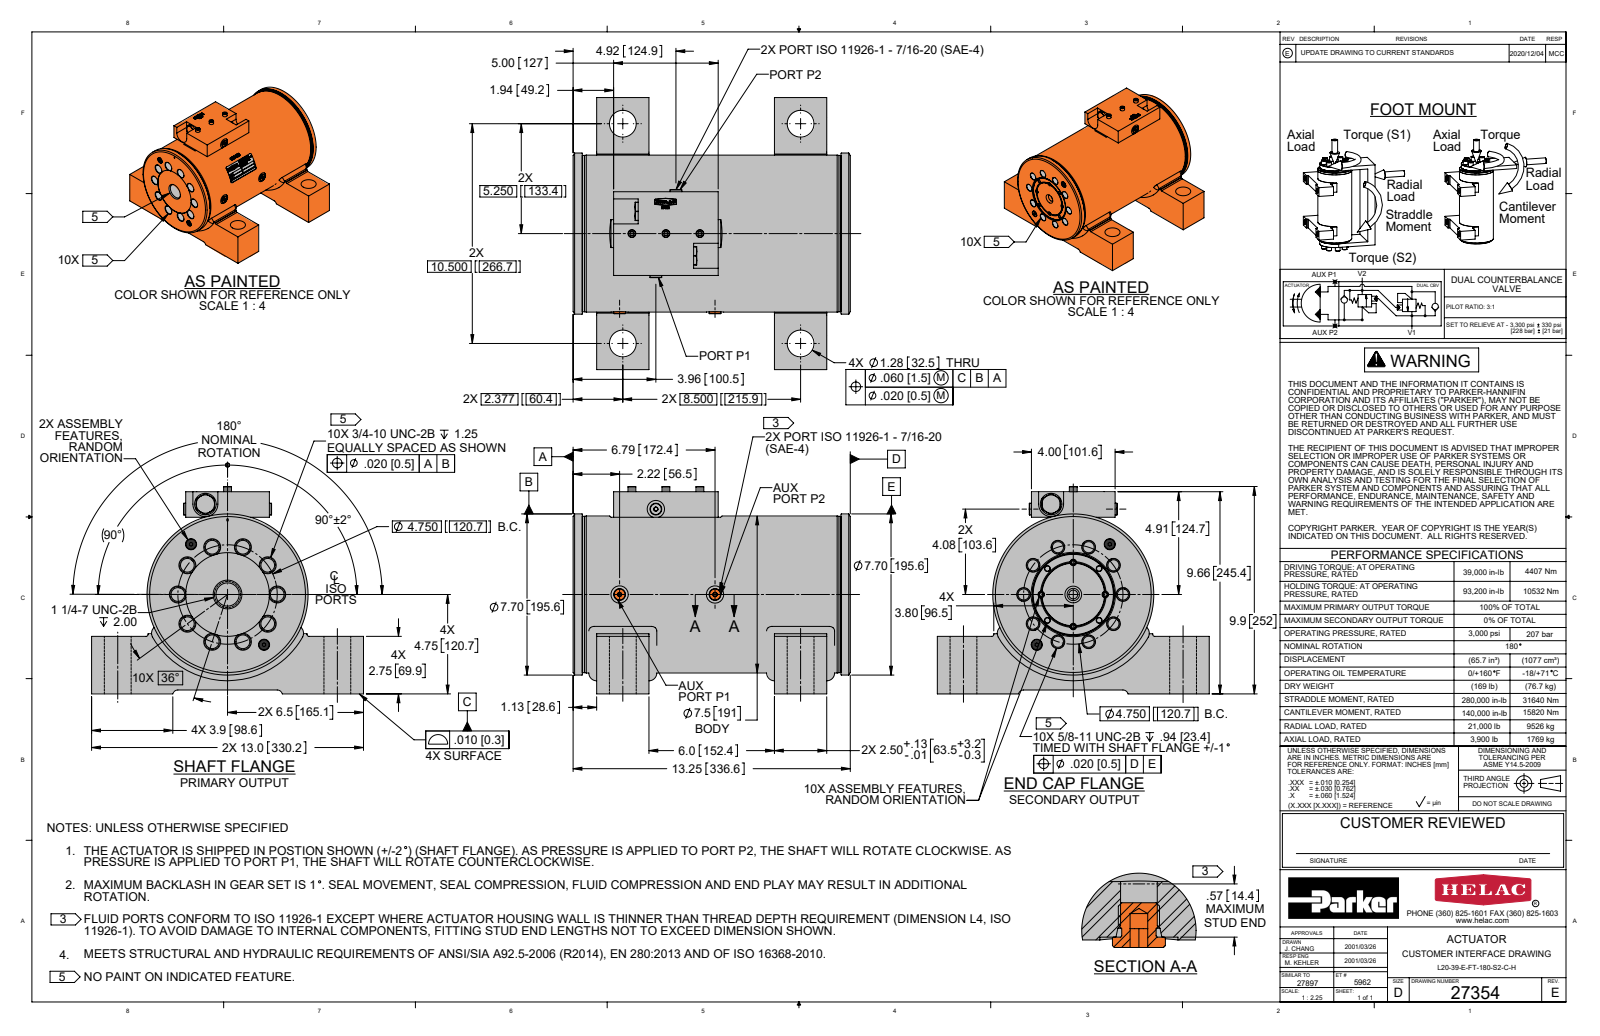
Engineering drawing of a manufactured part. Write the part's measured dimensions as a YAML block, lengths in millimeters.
part_name: "27354-CM.CYL"
step_written_by: "SolidWorks 2018 (AUTOMOTIVE_DESIGN)"
units: millimeters
bodies: {solids: 30, faces: 2219, planar: 515, cylindrical: 805, other: 899}
overall_size: [336.6, 330.2, 251.7]
volume: 12400000
surface_area: 1265000
round_holes:
  - {diameter: 13.5, count: 10}
  - {diameter: 15.9, count: 10}
  - {diameter: 16.7, count: 10}
  - {diameter: 19.1, count: 10}
  - {diameter: 6.4, count: 9}
  - {diameter: 4.7, count: 4}
  - {diameter: 8, count: 4}
  - {diameter: 32.5, count: 4}
  - {diameter: 5.2, count: 3}
  - {diameter: 6.8, count: 3}
  - {diameter: 4, count: 2}
  - {diameter: 4.8, count: 2}
round_bosses_or_shafts:
  - {diameter: 14.3, count: 4}
  - {diameter: 11.1, count: 4}
  - {diameter: 9.3, count: 4}
  - {diameter: 9.5, count: 3}
  - {diameter: 21.8, count: 2}
  - {diameter: 19.8, count: 2}
  - {diameter: 19.1, count: 2}
  - {diameter: 17.9, count: 2}
partial_cylinders:
  - {radius: 1.7, count: 12}
  - {radius: 0.8, count: 4}
  - {radius: 2.5, count: 4}
  - {radius: 2.4, count: 2}
  - {radius: 4.1, count: 2}
  - {radius: 6.4, count: 2}
  - {radius: 12.7, count: 2}
  - {radius: 15.2, count: 2}
face_to_face_distances: [215.9, 63.5, 152.4, 279.4, 28.6, 92.1, 244.5, 308, 214.4, 336.6]
hole_center_spacings: [37.3, 60.3, 114.7, 32.3, 70.9, 77, 97.6, 17.8]
